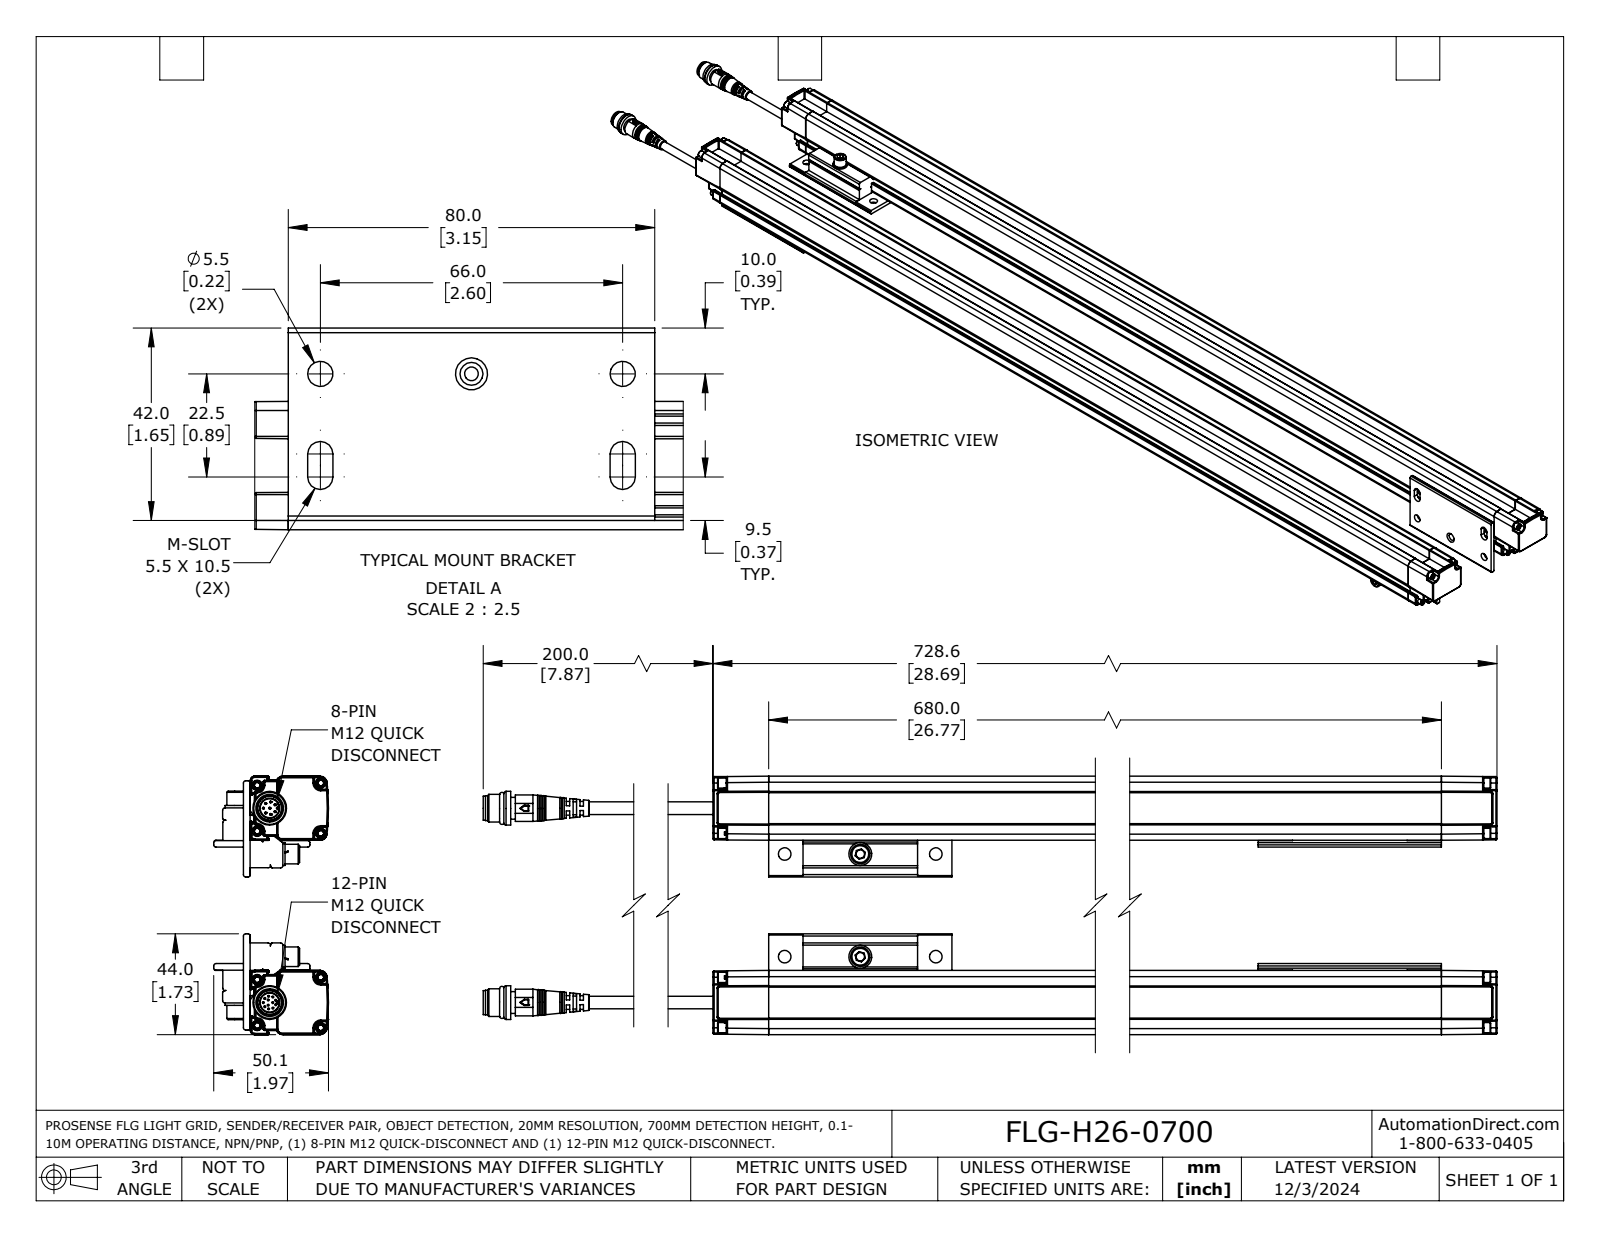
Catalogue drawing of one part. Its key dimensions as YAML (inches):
part_name: "FLG-H26-0700"
step_written_by: "SolidWorks 2023 (AUTOMOTIVE_DESIGN)"
units: inches
bodies: {solids: 10, faces: 1668, planar: 816, cylindrical: 456, other: 396}
overall_size: [32.305, 4.441, 1.972]
volume: 73.41
surface_area: 485.4
round_holes:
  - {diameter: 0.016, count: 16}
  - {diameter: 0.217, count: 6}
  - {diameter: 0.098, count: 4}
  - {diameter: 0.197, count: 3}
  - {diameter: 0.327, count: 2}
round_bosses_or_shafts:
  - {diameter: 0.031, count: 20}
  - {diameter: 0.177, count: 8}
  - {diameter: 0.118, count: 8}
  - {diameter: 0.217, count: 4}
  - {diameter: 0.059, count: 4}
  - {diameter: 0.394, count: 3}
  - {diameter: 0.335, count: 3}
  - {diameter: 0.146, count: 3}
partial_cylinders:
  - {radius: 0.02, count: 142}
  - {radius: 0.039, count: 40}
  - {radius: 0.01, count: 20}
  - {radius: 0.008, count: 12}
  - {radius: 0.012, count: 12}
  - {radius: 0.108, count: 12}
  - {radius: 0.1, count: 6}
  - {radius: 0.049, count: 4}
face_to_face_distances: [3.339, 1.102, 0.071, 0.285, 0.817, 2.236, 0.97, 4.441, 1.041, 0.118]
hole_center_spacings: [0.108, 1.299, 0.163, 0.979, 2.191, 0.215, 1.764, 2.598]
